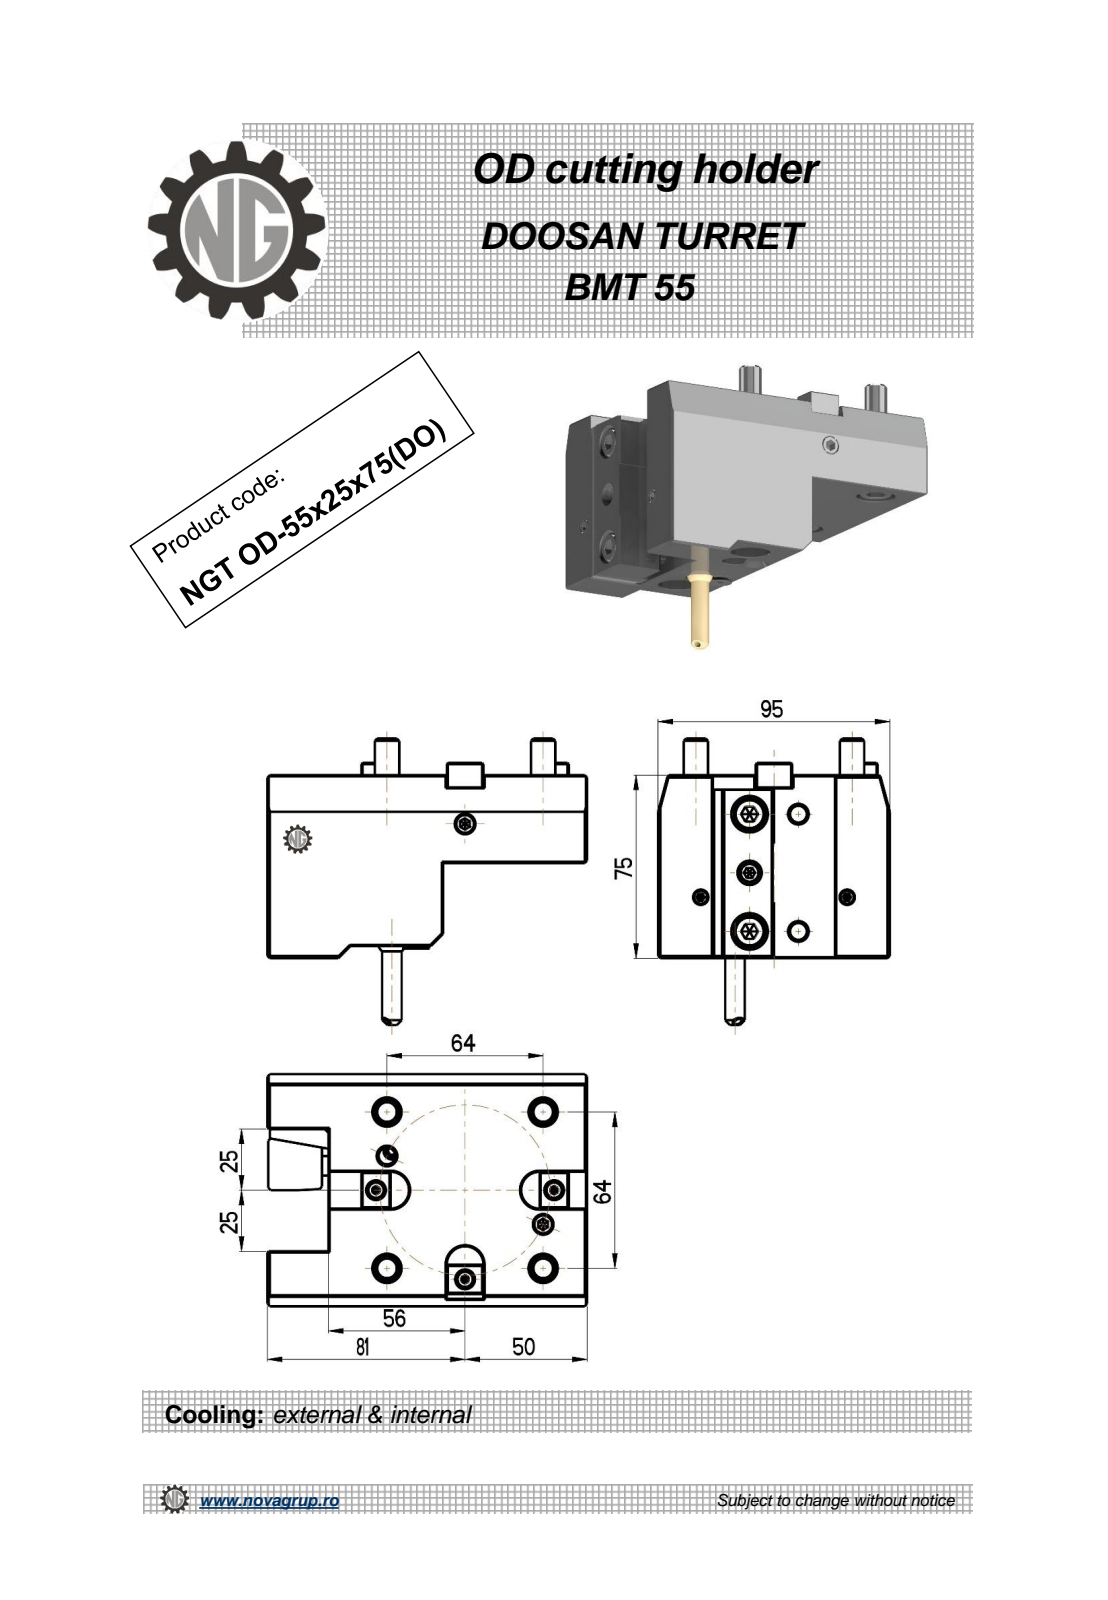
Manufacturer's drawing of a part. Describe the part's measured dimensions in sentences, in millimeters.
The part is named "NGT_OD_55_25_75_DO". Its 3-D file was written by "PRO/ENGINEER BY PARAMETRIC TECHNOLOGY CORPORATION, 2010280 (CONFIG_CONTROL_DESIGN)". It is 1 solid with 239 faces: 167 planar, 38 cylindrical and 34 other. Overall it measures 131 by 117.34 by 95 millimeters. Its volume is 635 401 cubic millimeters and its surface area 62 030 square millimeters. Round holes: 1 of diameter 3, 1 of diameter 5, 1 of diameter 6.8. Round bosses or shafts: 4 of diameter 10, 4 of diameter 8, 1 of diameter 11.2. Partial cylindrical surfaces (rounded edges, fillets, slot ends): 6 of radius 0.22, 6 of radius 0.41, 3 of radius 7.5. The main face-to-face distances are 36, 95, 25, 70, 47, 106, 131, 34, 72, 59. The hole center spacings are 2.83.
